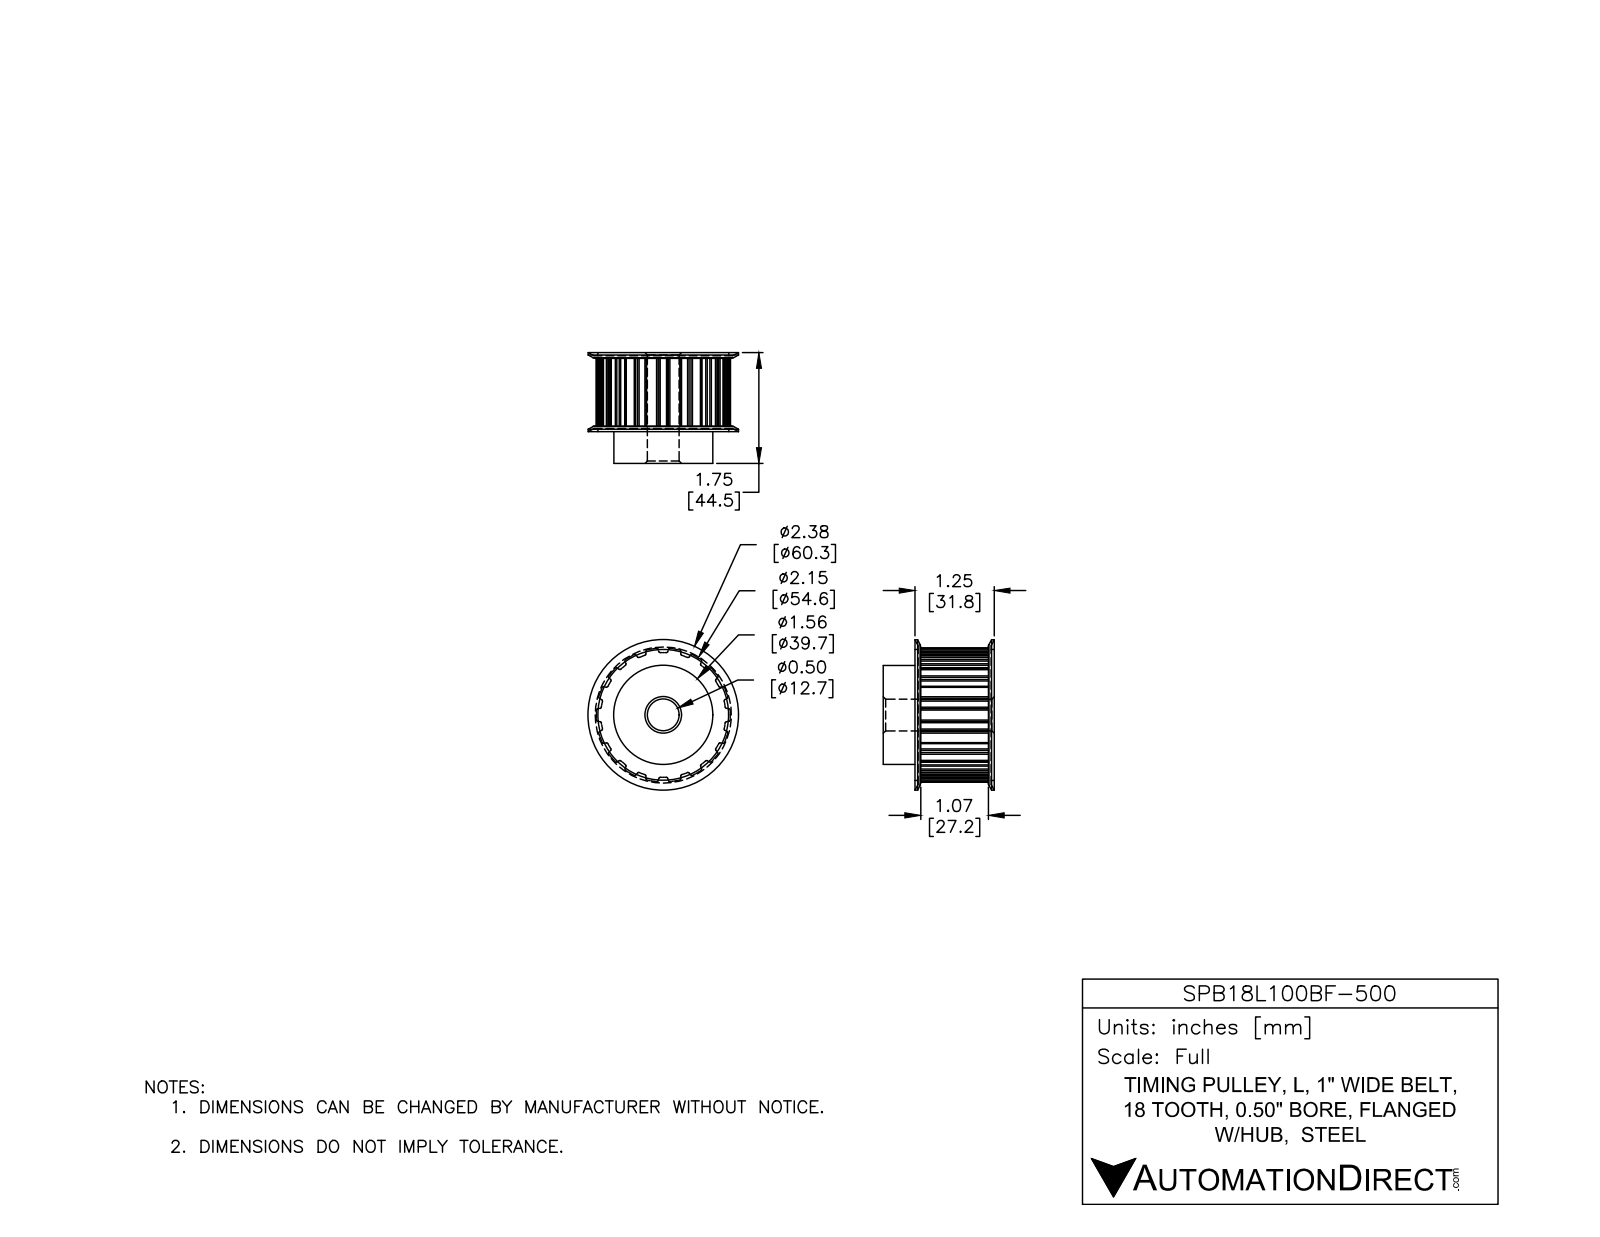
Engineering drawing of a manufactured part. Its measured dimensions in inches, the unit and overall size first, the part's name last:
Units: inches
Overall size (bounding box): 2.375 × 2.375 × 1.75
Round holes (diameter × count): ⌀0.5 ×1
Round bosses / shafts (diameter × count): ⌀2.375 ×1, ⌀2.066 ×1, ⌀1.563 ×1
Partial cylindrical surfaces — rounded edges, fillets, slot ends (radius × count): R0.02 ×72, R1.059 ×1
Main face-to-face distances: 1.75, 1.25, 0.5, 1.969, 0.05, 1.2, 0.553, 0.09, 1.16, 0.04
Volume: 4.856 in³ · Surface area: 26.14 in²
Bodies: 1 solid, 192 faces (61 planar, 115 cylindrical, 16 other)
Part name (STEP PRODUCT): SPB18L100BF-500
STEP written by: SolidWorks 2015 (AUTOMOTIVE_DESIGN)
